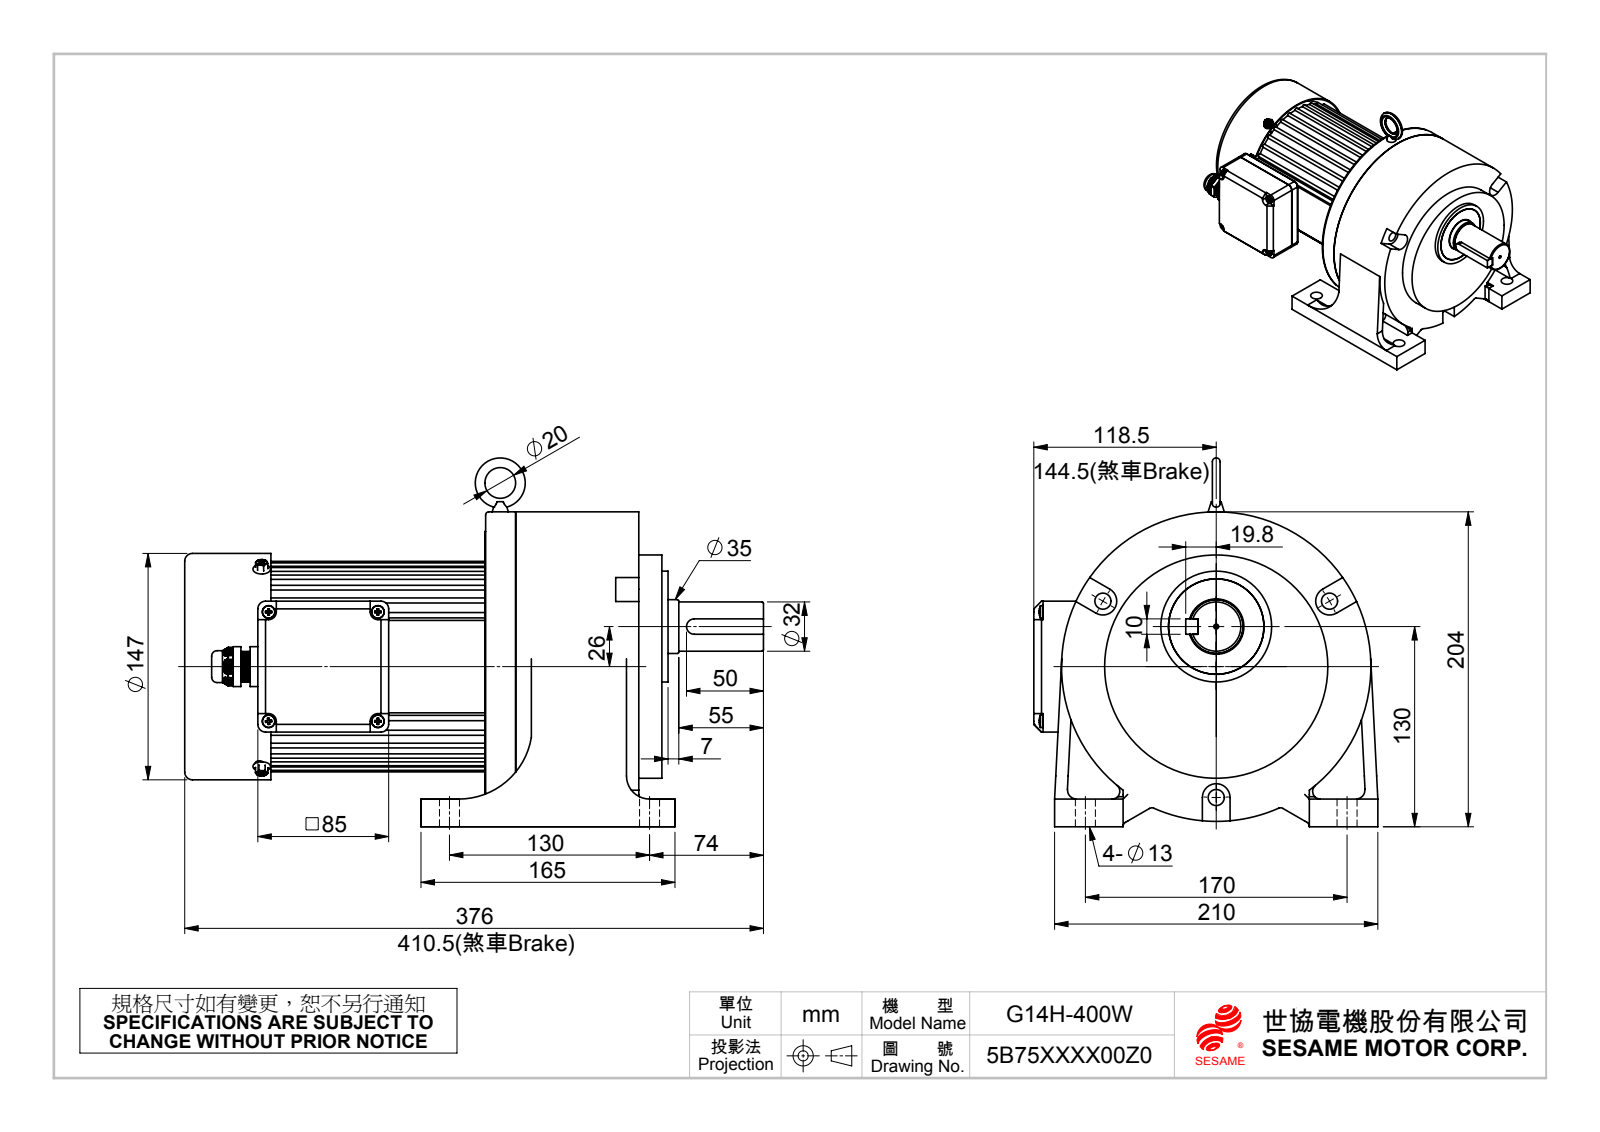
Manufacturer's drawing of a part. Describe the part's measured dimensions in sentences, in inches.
The part is named "出線盒墊片JTH-UP3(PVC2mm厚); G140S1; 10x8xL_50L; (標準品)G14H400W(5B75XXX100)(減速比共用) (+8 more)". Its 3-D file was written by "SolidWorks 2010 (CONFIG_CONTROL_DESIGN)". It is 20 solids with 2669 faces: 832 planar, 826 cylindrical and 1011 other. Overall it measures 14.803 by 9.429 by 8.799 inches. Its volume is 399.4 cubic inches and its surface area 897 square inches. Round holes: 14 of diameter 0.197, 9 of diameter 0.13, 5 of diameter 0.236, 4 of diameter 0.315, 4 of diameter 0.512, 3 of diameter 0.413, 3 of diameter 0.591, 1 of diameter 0.079, 1 of diameter 0.268, 1 of diameter 0.425, 1 of diameter 0.65, 1 of diameter 0.787. Round bosses or shafts: 4 of diameter 0.327, 4 of diameter 0.157, 2 of diameter 0.197, 1 of diameter 7.913, 1 of diameter 6.908, 1 of diameter 5.787, 1 of diameter 5.197, 1 of diameter 4.937. Partial cylindrical surfaces (rounded edges, fillets, slot ends): 31 of radius 0.073, 26 of radius 0.039, 24 of radius 0.02, 11 of radius 0.197, 10 of radius 0.118, 6 of radius 0.108, 4 of radius 0.079, 4 of radius 0.1. The main face-to-face distances are 0.984, 0.709, 0.079, 5.512, 6.496, 1.752, 0.591, 9.449, 3.937, 2.953. The hole center spacings are 1.772, 2.507, 2.795, 3.346, 5.796, 0.433, 0.453, 0.575.
